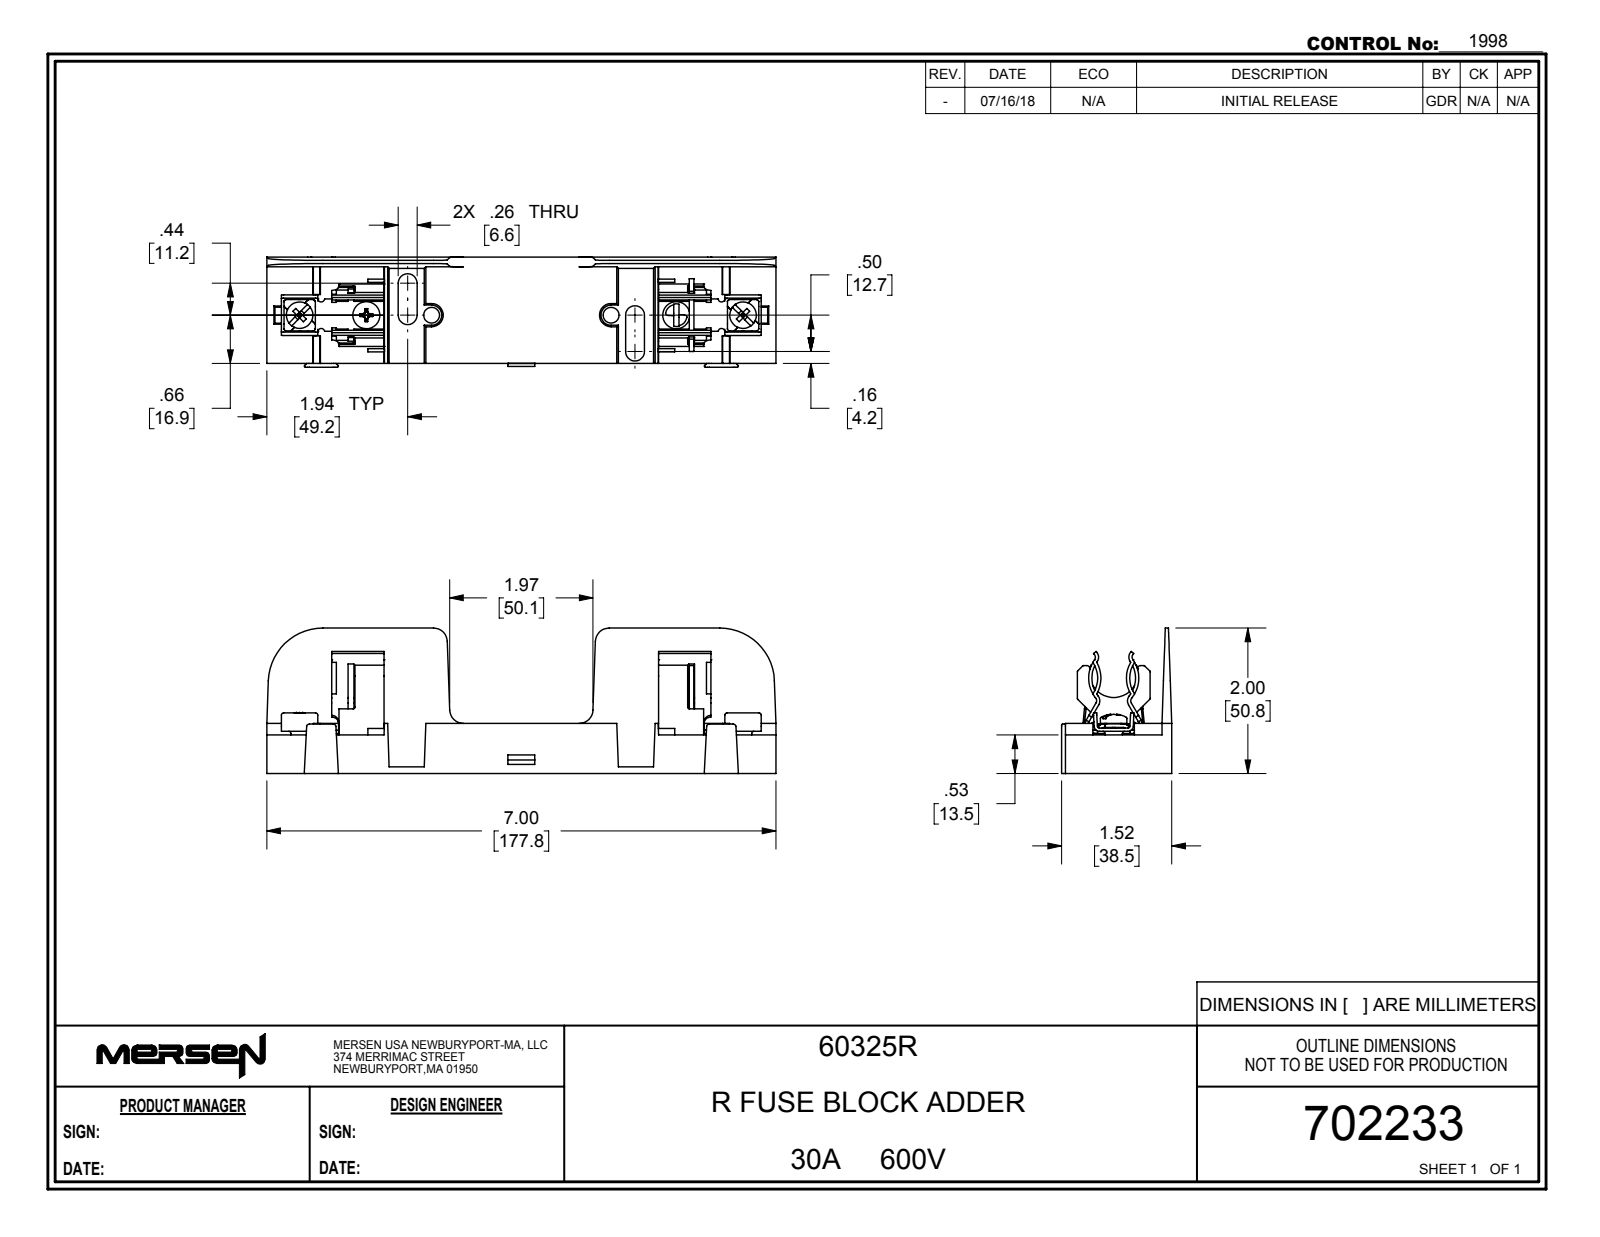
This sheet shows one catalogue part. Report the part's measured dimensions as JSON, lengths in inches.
{"part_name": "702233rev", "step_written_by": "SolidWorks 2017 (AUTOMOTIVE_DESIGN)", "units": "inches", "bodies": {"solids": 12, "faces": 1054, "planar": 616, "cylindrical": 273, "other": 165}, "overall_size": [7, 2, 1.515], "volume_in3": 3.687, "surface_area_in2": 85.26, "round_holes": [[0.159, 2], [0.218, 2]], "round_bosses_or_shafts": [[0.373, 2], [0.239, 2], [0.19, 2], [0.156, 2], [0.365, 1], [0.365, 1], [0.115, 1]], "partial_cylinders_radius": [[0.01, 18], [0.02, 18], [0.004, 12], [0.07, 12], [0.02, 11], [0.015, 10], [0.03, 10], [0.032, 8]], "face_to_face_distances": [0.02, 1.463, 0.53, 0.16, 0.69, 0.12, 0.04, 0.11, 0.15, 0.57], "hole_center_spacings": [1.815, 4.283, 2.468, 6.097]}
